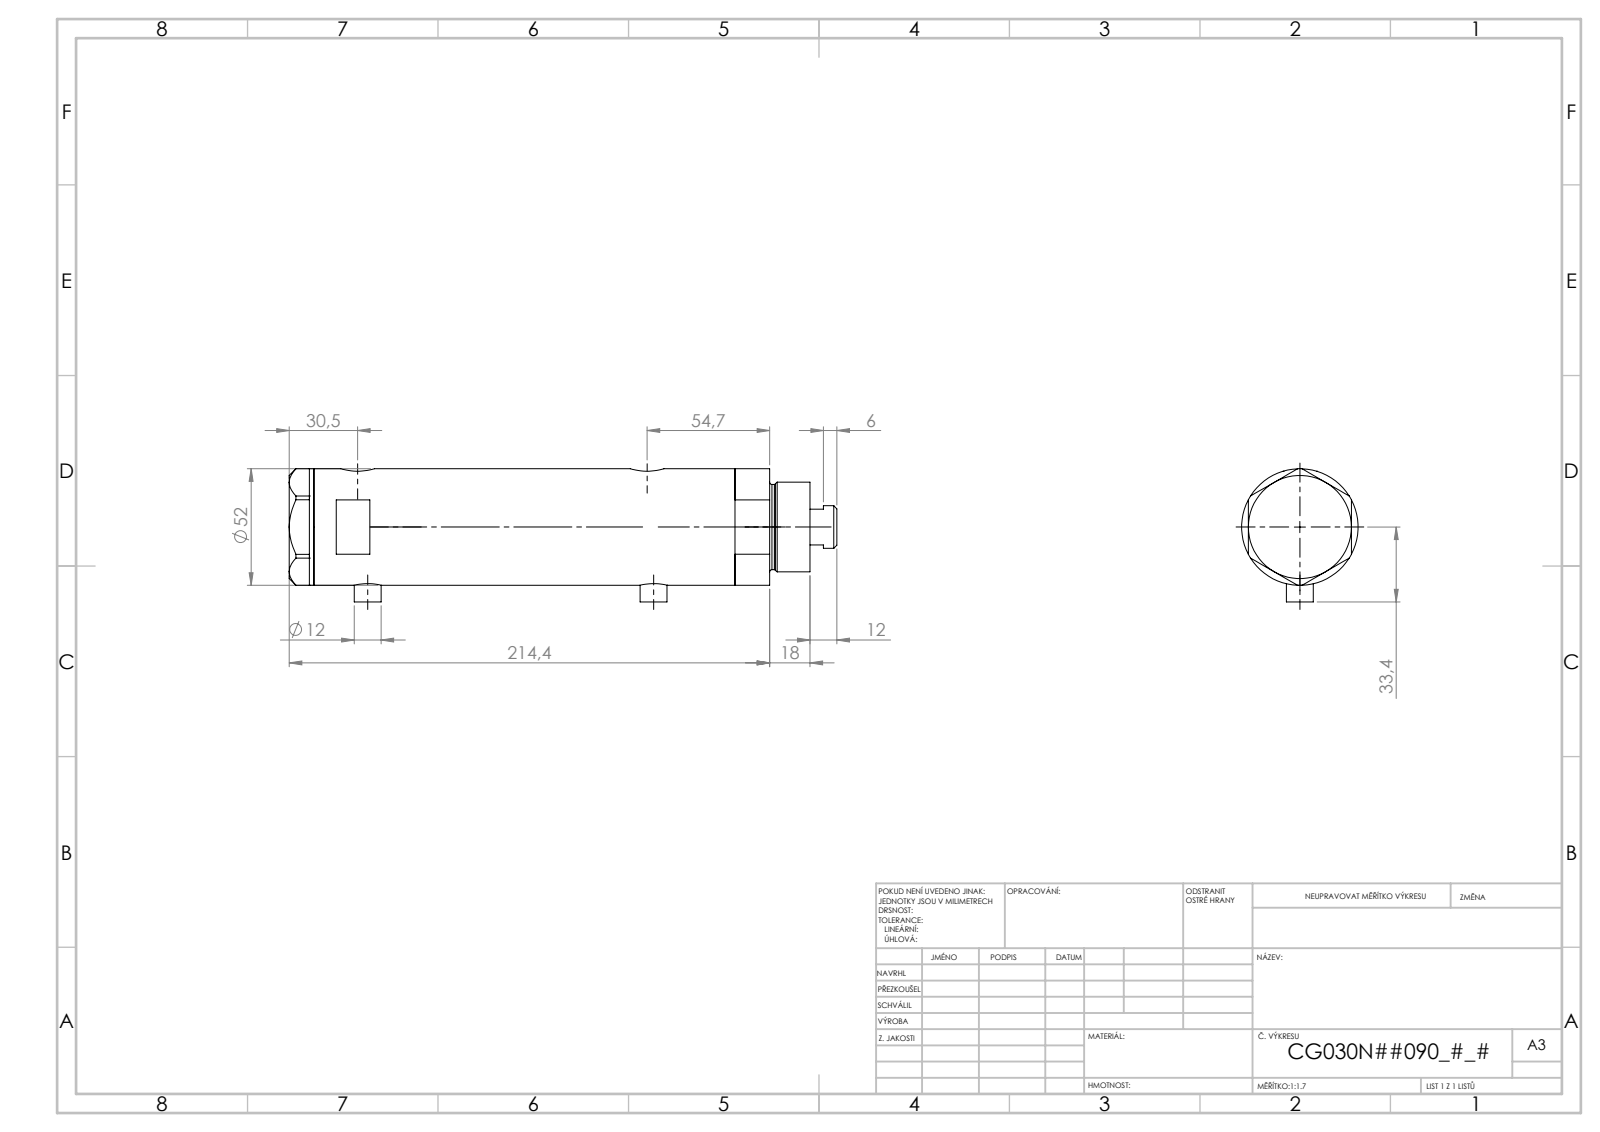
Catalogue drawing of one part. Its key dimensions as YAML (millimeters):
part_name: "V270CG_BACK; V270CG_MIDDLE; V270CG_VC; V270CG_FRONT"
step_written_by: "SolidWorks 2019 (CONFIG_CONTROL_DESIGN)"
units: millimeters
bodies: {solids: 4, faces: 140, planar: 67, cylindrical: 53, other: 20}
overall_size: [239.02, 53.1, 52]
volume: 423310
surface_area: 93929
round_holes:
  - {diameter: 5, count: 2}
  - {diameter: 9.73, count: 2}
  - {diameter: 12.5, count: 2}
  - {diameter: 15, count: 2}
  - {diameter: 6.5, count: 1}
  - {diameter: 20, count: 1}
  - {diameter: 21.5, count: 1}
  - {diameter: 30, count: 1}
  - {diameter: 33, count: 1}
  - {diameter: 44, count: 1}
round_bosses_or_shafts:
  - {diameter: 12, count: 2}
  - {diameter: 52, count: 1}
  - {diameter: 40, count: 1}
  - {diameter: 38, count: 1}
  - {diameter: 19, count: 1}
face_to_face_distances: [143.54, 23.8, 119.74, 11, 34.8, 154.54, 46, 190.94, 179.94, 156.14]
hole_center_spacings: [2.9, 4.5, 116.75, 119.65, 121.25, 124.15, 2.89, 2.91]
